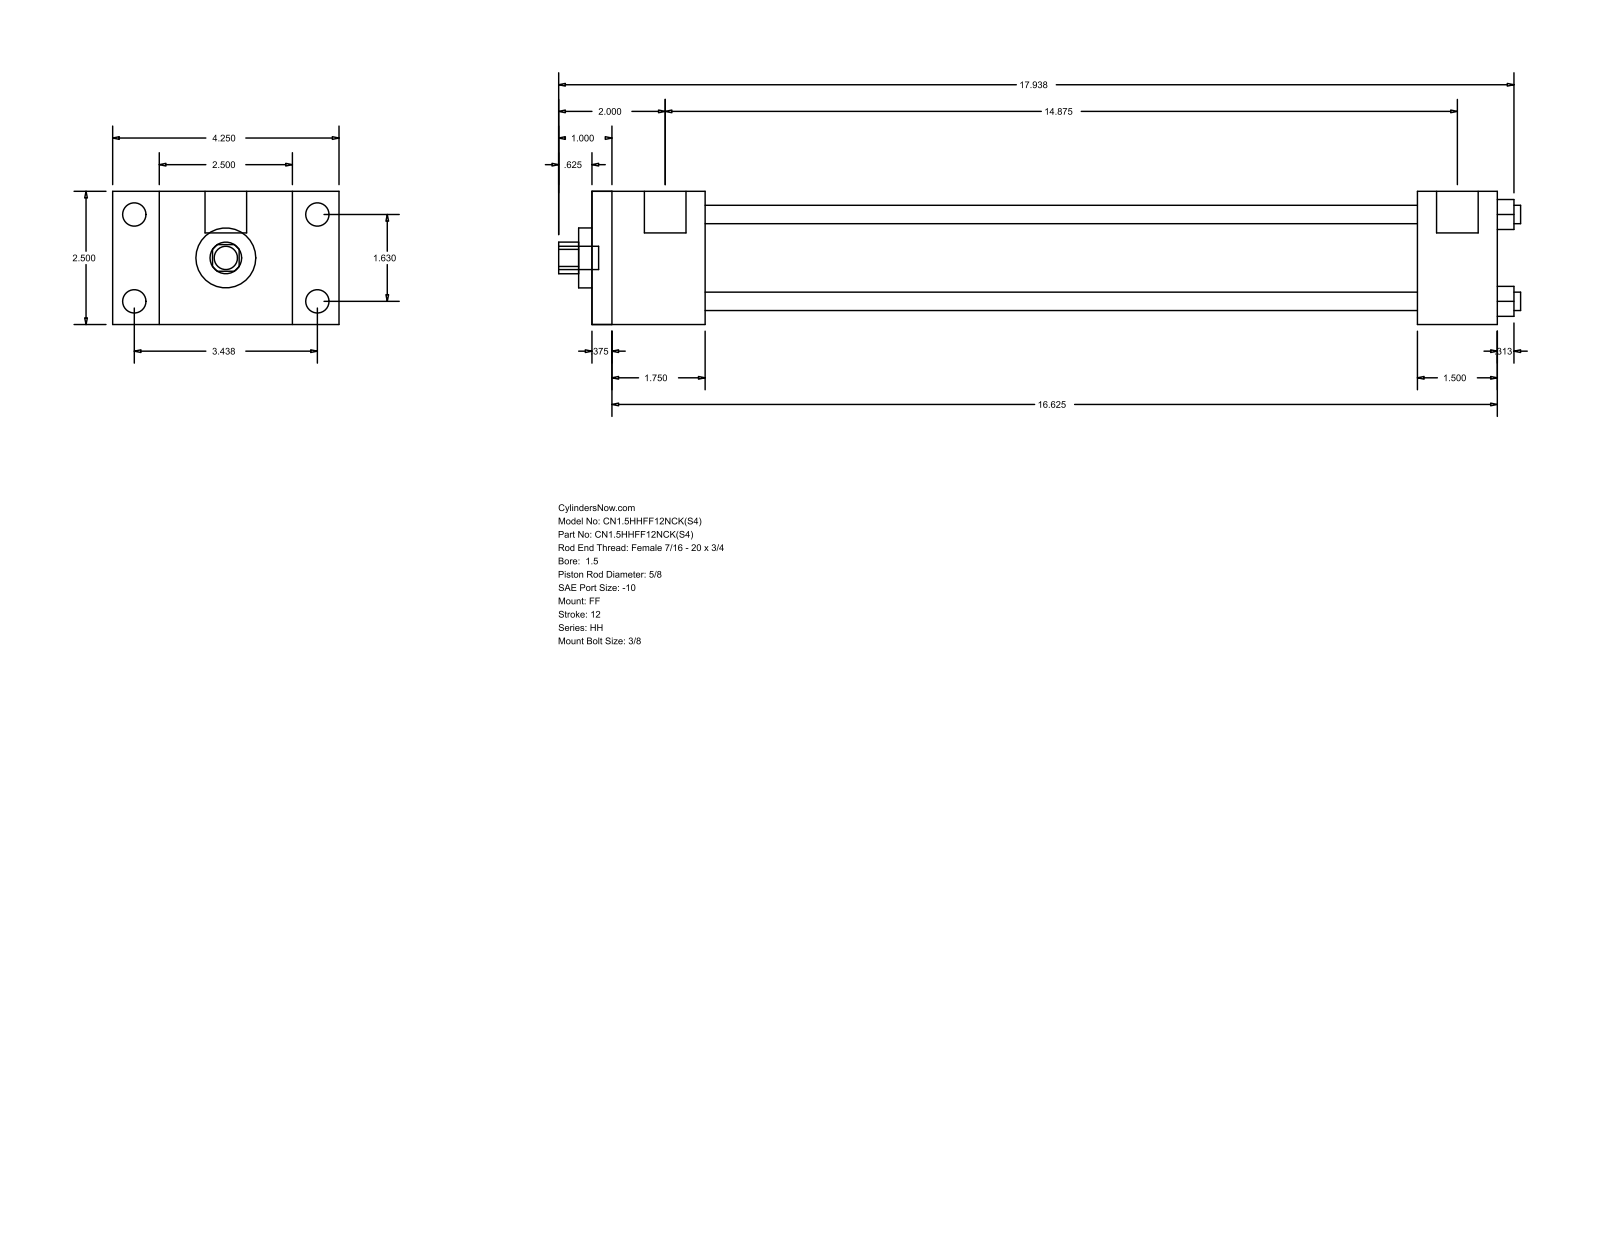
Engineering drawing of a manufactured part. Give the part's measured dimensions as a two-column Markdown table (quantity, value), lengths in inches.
| quantity | value |
| --- | --- |
| part name | HH_FF__0150_0.625 |
| STEP written by | GSSL Pune (CONFIG_CONTROL_DESIGN) |
| units | inches |
| bodies | 0 solids, 92 faces (64 planar, 28 cylindrical, 0 other) |
| overall size | 18.063 × 4.25 × 2.5 |
| round holes (diameter × count) | 0.345 × 4, 0.625 × 1, 1.125 × 1, 1.75 × 1 |
| round bosses / shafts (diameter × count) | 0.438 × 4, 0.219 × 4, 0.781 × 2, 0.437 × 1 |
| partial cylindrical surfaces (radius × count) | 0.297 × 1 |
| main face-to-face distances | 2.5, 17, 0.375, 16.625, 2.125, 1.75, 14.875, 15.5, 15.125, 13.375 |
| hole center spacings | 1.152, 1.63, 2.305 |
